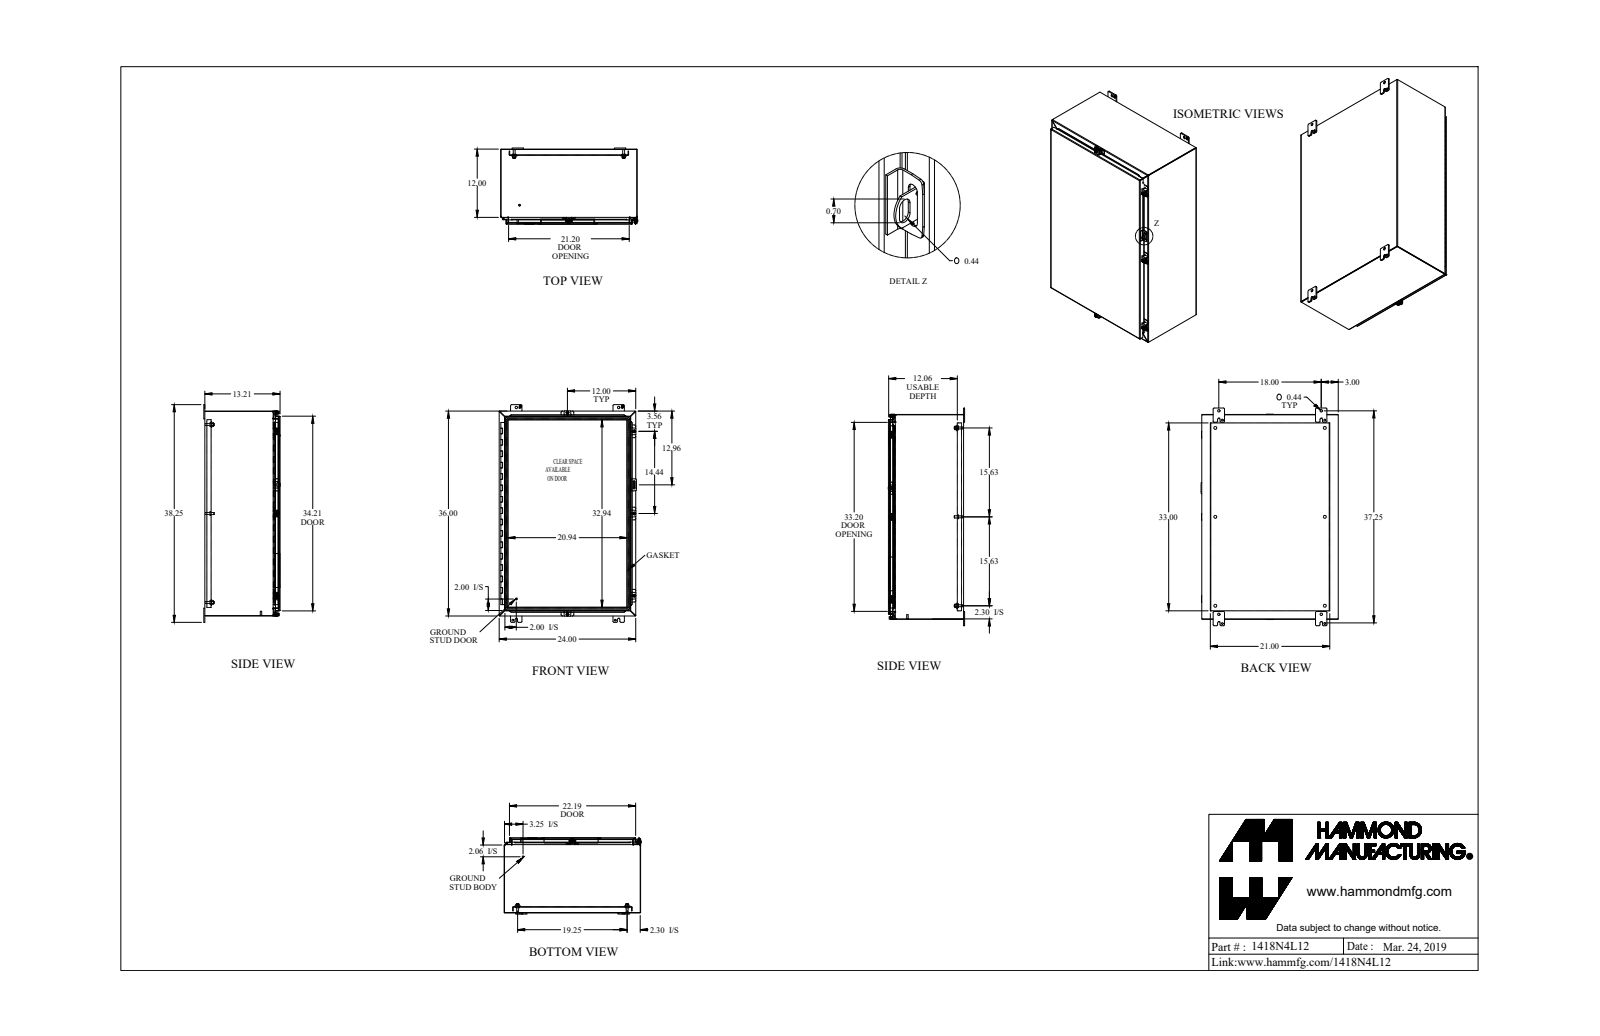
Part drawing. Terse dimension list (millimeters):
name: 1418N4L12_Default
written by: SolidWorks 2019 (CONFIG_CONTROL_DESIGN)
unit: mm
bodies: 53 solids, 1737 faces (1011 planar, 616 cylindrical, 110 other)
size: 971.6 × 612.8 × 341.3
volume: 5 550 000 mm³; area: 5 744 000 mm²
holes: 6× ⌀12.7, 5× ⌀5.4, 5× ⌀7.8, 4× ⌀6.7, 4× ⌀8, 4× ⌀9.5, 4× ⌀11.1, 4× ⌀11.3, 1× ⌀3.2, 1× ⌀4.7, 1× ⌀6.7, 1× ⌀9.5
bosses: 6× ⌀16.5, 6× ⌀9.5, 6× ⌀8.4, 5× ⌀25.4, 5× ⌀12.7, 5× ⌀9.9, 5× ⌀6.2, 2× ⌀7.1
rounds: 28× R6.4, 27× R1.2, 27× R3.6, 26× R4.8, 22× R0.9, 22× R2.7, 10× R3.2, 10× R3.6
face distances: 1.8, 1.8, 607.8, 331.9, 333.7, 333.7, 335.5, 307.5, 305.7, 26.2
hole spacings: 489, 793.8, 932.3, 250.4, 250.4, 396.9, 396.9, 629.7
